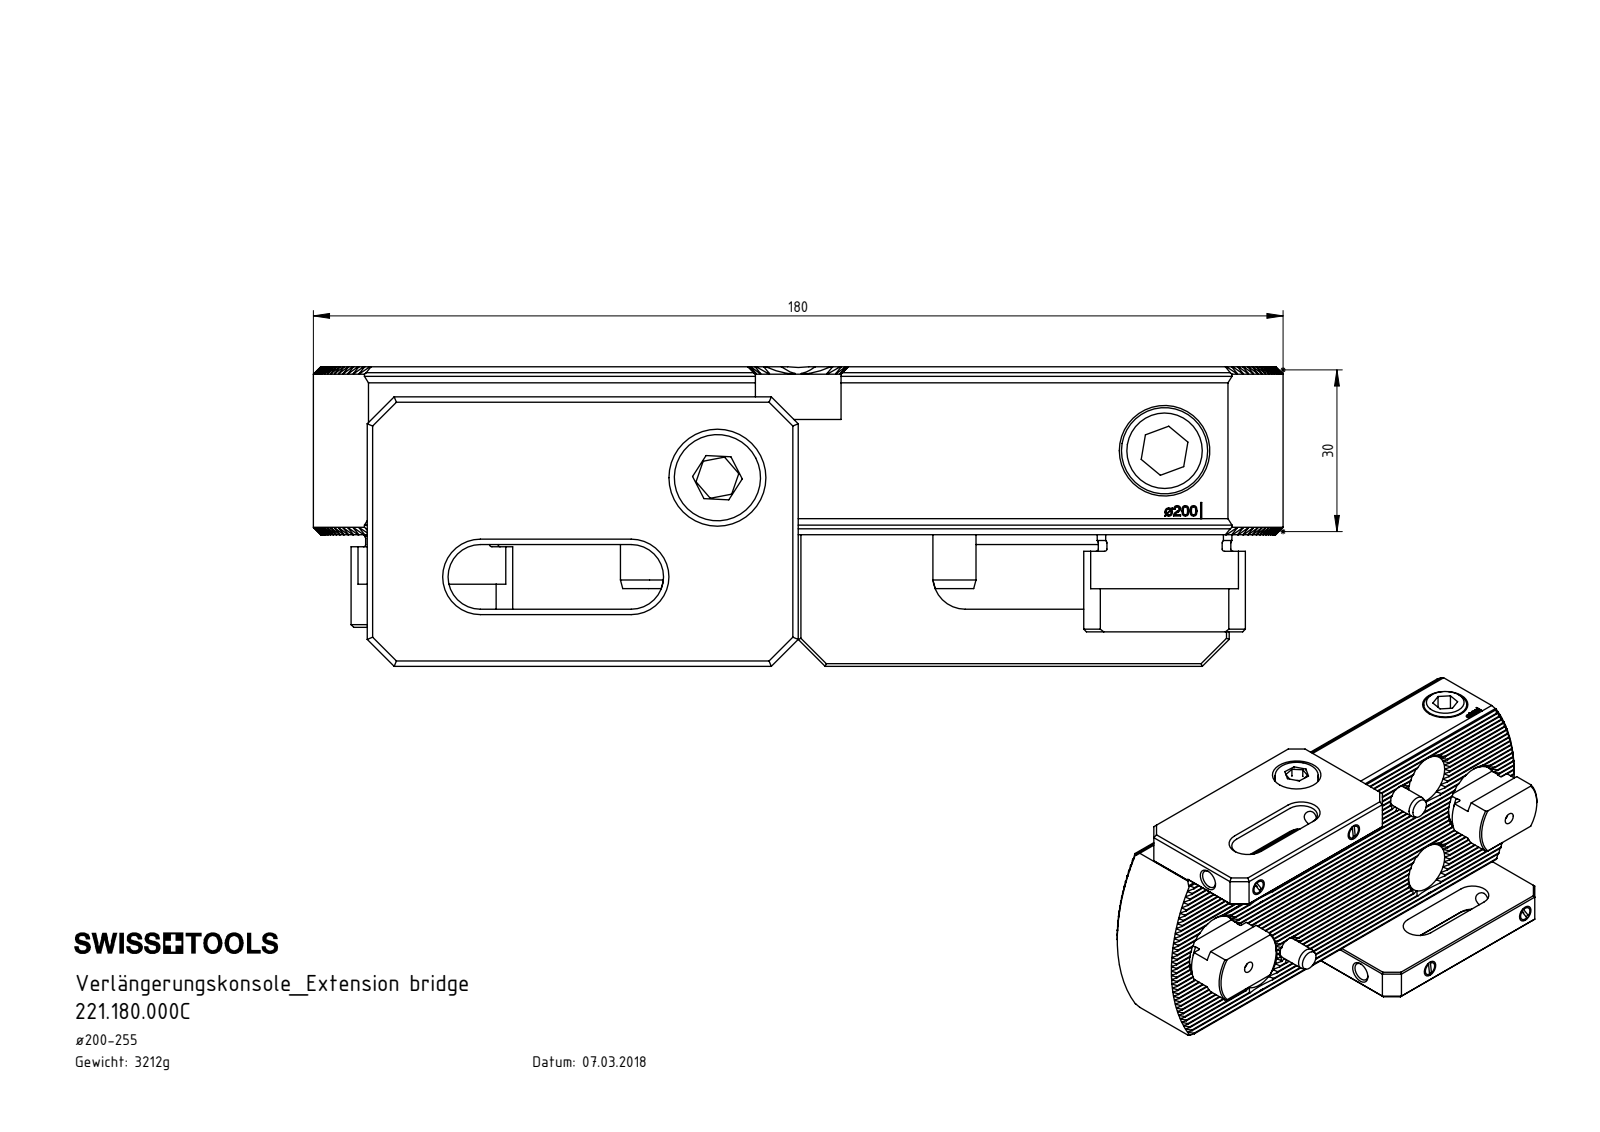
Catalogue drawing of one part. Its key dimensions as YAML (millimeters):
part_name: "Ko1-VK1.180.030_C; VK1-ER3.001.028_A; VK1-ER7.001.012; ISO 4766 - M6x12_ISO 4766 - M6 x 10 (+8 more)"
step_written_by: "SolidWorks 2017 (CONFIG_CONTROL_DESIGN)"
units: millimeters
bodies: {solids: 25, faces: 1771, planar: 971, cylindrical: 477, other: 323}
overall_size: [180, 95, 55.58]
volume: 418741
surface_area: 114296
round_holes:
  - {diameter: 5, count: 4}
  - {diameter: 6, count: 4}
  - {diameter: 6.8, count: 4}
  - {diameter: 13, count: 4}
  - {diameter: 19, count: 4}
  - {diameter: 2, count: 2}
  - {diameter: 8, count: 2}
  - {diameter: 8.5, count: 2}
  - {diameter: 10.5, count: 2}
  - {diameter: 11, count: 2}
  - {diameter: 14, count: 2}
  - {diameter: 18, count: 2}
round_bosses_or_shafts:
  - {diameter: 16, count: 4}
  - {diameter: 6, count: 4}
  - {diameter: 10, count: 2}
partial_cylinders:
  - {radius: 0.14, count: 66}
  - {radius: 2, count: 8}
  - {radius: 6, count: 4}
  - {radius: 12.3, count: 2}
  - {radius: 15, count: 2}
  - {radius: 65, count: 2}
  - {radius: 7.95, count: 1}
face_to_face_distances: [12, 82, 70, 1.73, 0.5, 82.5, 11.5, 70.5, 94, 3.46]
hole_center_spacings: [31.24, 113.77, 136, 7.9, 15, 18.55, 19.61, 31.89]
